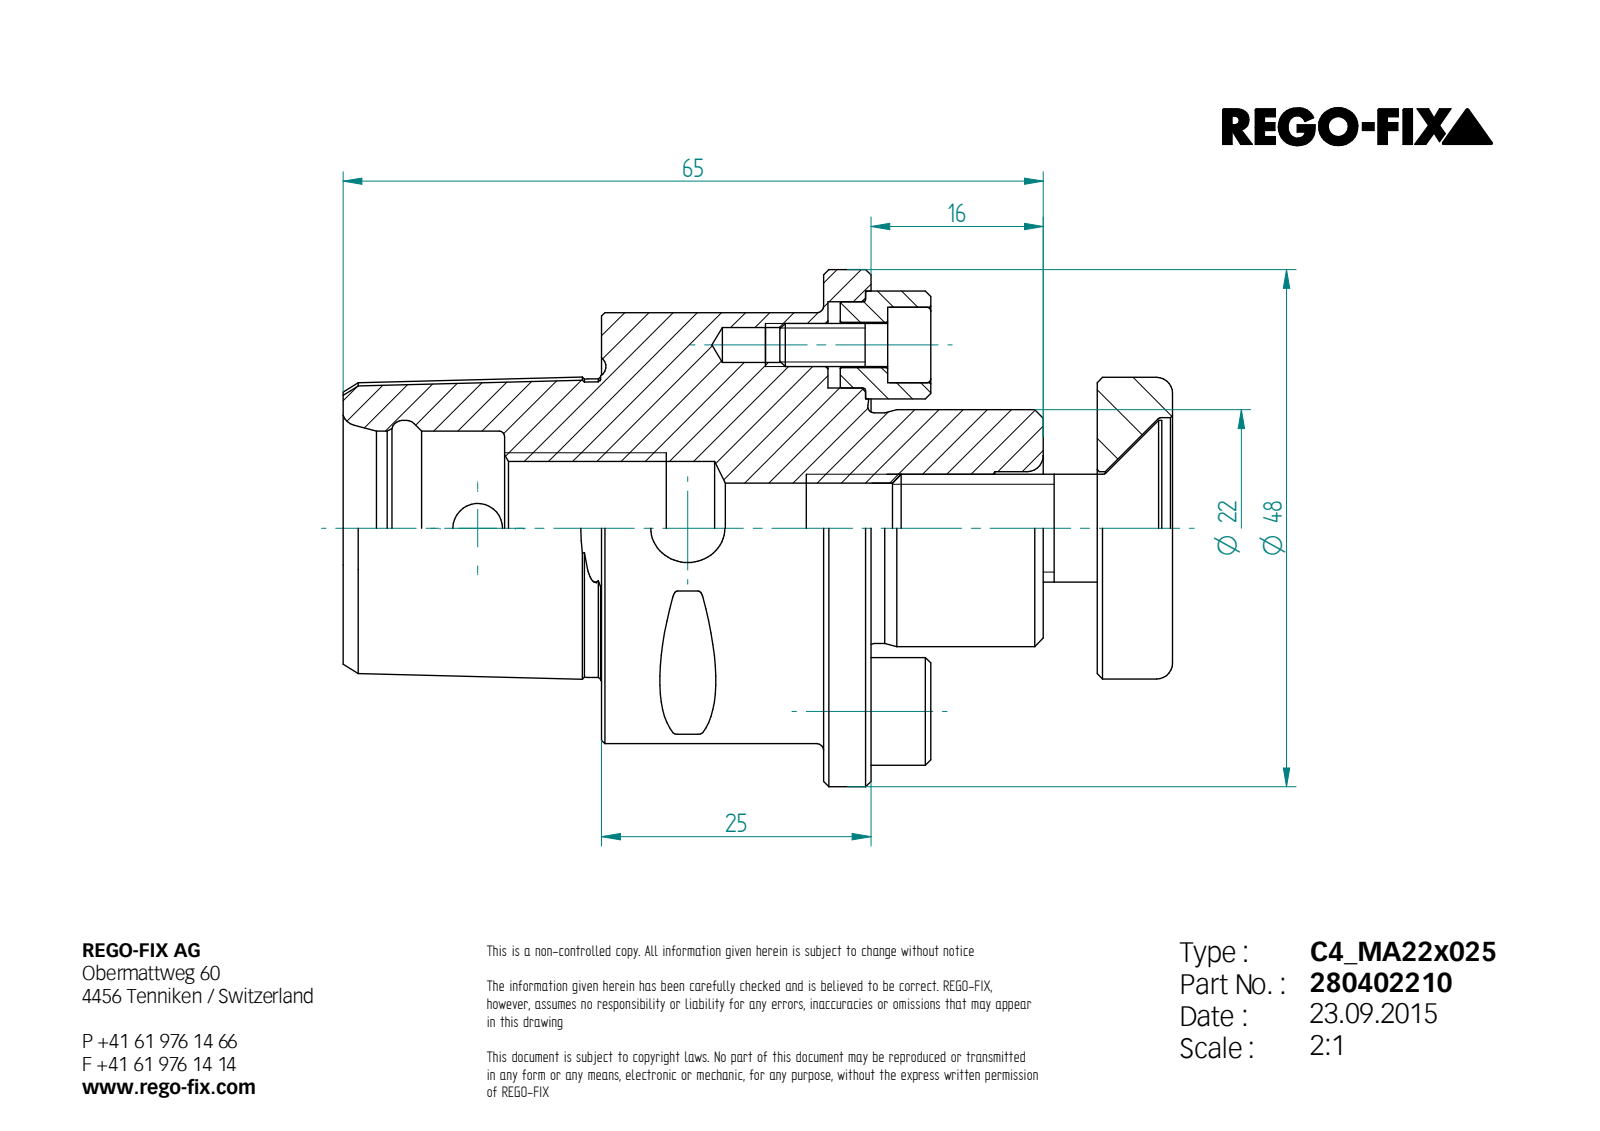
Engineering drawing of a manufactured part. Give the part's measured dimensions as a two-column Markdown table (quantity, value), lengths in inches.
| quantity | value |
| --- | --- |
| part name | 0002763; 0003451; 0003387; 0010452 (+1 more) |
| STEP written by | Unknown (AUTOMOTIVE_DESIGN) |
| units | inches |
| bodies | 7 solids, 225 faces (68 planar, 52 cylindrical, 105 other) |
| overall size | 3.031 × 1.89 × 1.89 |
| volume | 3.09 in³ |
| surface area | 27.25 in² |
| round holes (diameter × count) | 0.127 × 2, 0.128 × 2, 0.165 × 2, 0.276 × 2, 0.315 × 2, 0.394 × 2, 0.157 × 1, 0.181 × 1, 0.33 × 1, 0.413 × 1, 0.487 × 1, 0.709 × 1 |
| round bosses / shafts (diameter × count) | 0.157 × 2, 1.89 × 1, 1.575 × 1, 1.102 × 1, 0.866 × 1, 0.843 × 1, 0.394 × 1 |
| partial cylindrical surfaces (radius × count) | 0.02 × 8, 0.118 × 1 |
| main face-to-face distances | 0.827, 0.984, 0.173, 1.811, 0.811, 1, 0.236, 1.063, 2.047, 1.236 |
| hole center spacings | 0.669, 0.925, 1.339 |
